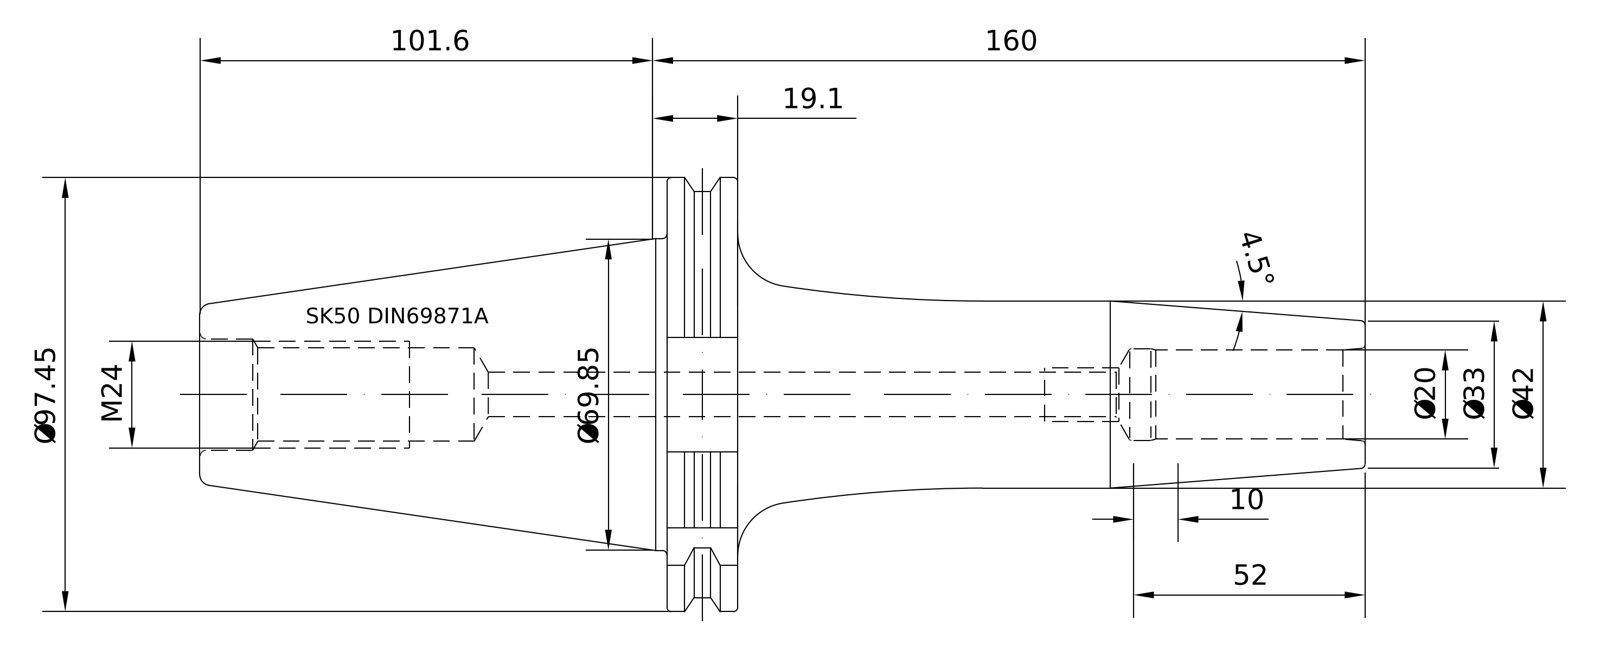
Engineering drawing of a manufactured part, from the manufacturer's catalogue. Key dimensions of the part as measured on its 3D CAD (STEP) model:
Part name (STEP PRODUCT): 50-442-20
STEP written by: PRO/ENGINEER BY PARAMETRIC TECHNOLOGY CORPORATION, 2010430 (CONFIG_CONTROL_DESIGN)
Units: millimetres
Bodies: 1 solid, 95 faces (21 planar, 24 cylindrical, 50 other)
Overall size (bounding box): 261.6 × 97.47 × 94
Volume: 519 317 mm³ · Surface area: 62 519 mm²
Round holes (diameter × count): ⌀20 ×1, ⌀20.75 ×1, ⌀25.01 ×1, ⌀25.7 ×1
Round bosses / shafts (diameter × count): ⌀91 ×1, ⌀69.15 ×1, ⌀42 ×1, ⌀24.01 ×1
Partial cylindrical surfaces — rounded edges, fillets, slot ends (radius × count): R1.75 ×1, R48.74 ×1
Main face-to-face distances: 15.85, 104.8, 156.8, 140.95, 72.8, 120.65, 261.6, 209.6, 88.95, 52
